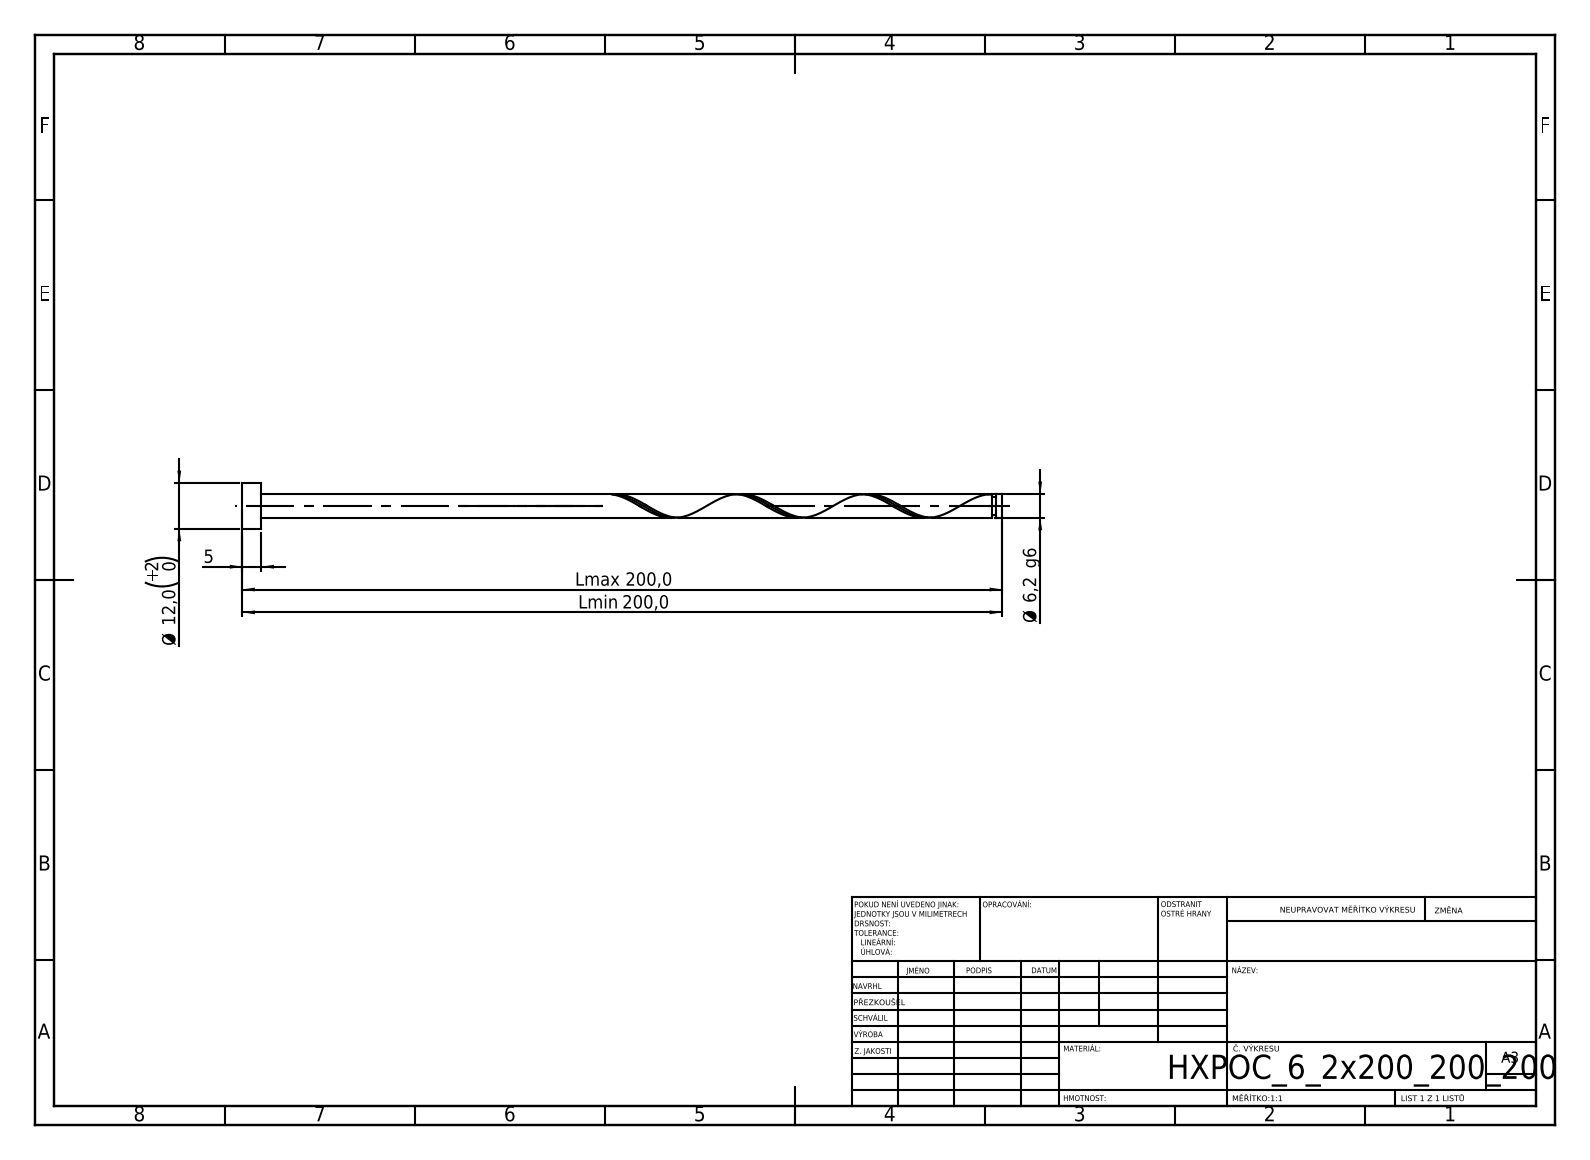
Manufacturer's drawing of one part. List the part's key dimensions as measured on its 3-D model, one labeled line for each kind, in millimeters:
STEP written by: SolidWorks 2019 (CONFIG_CONTROL_DESIGN)
Units: millimetres
Bodies: 1 solid, 21 faces (6 planar, 14 cylindrical, 1 other)
Overall size (bounding box): 200 × 12 × 12
Volume: 6 381 mm³ · Surface area: 4 302 mm²
Round bosses / shafts (diameter × count): ⌀12 ×1, ⌀6.2 ×1, ⌀4.96 ×1
Main face-to-face distances: 5, 200, 195, 198.44, 193.44, 1.56, 197.2, 192.2, 1.24, 2.8
